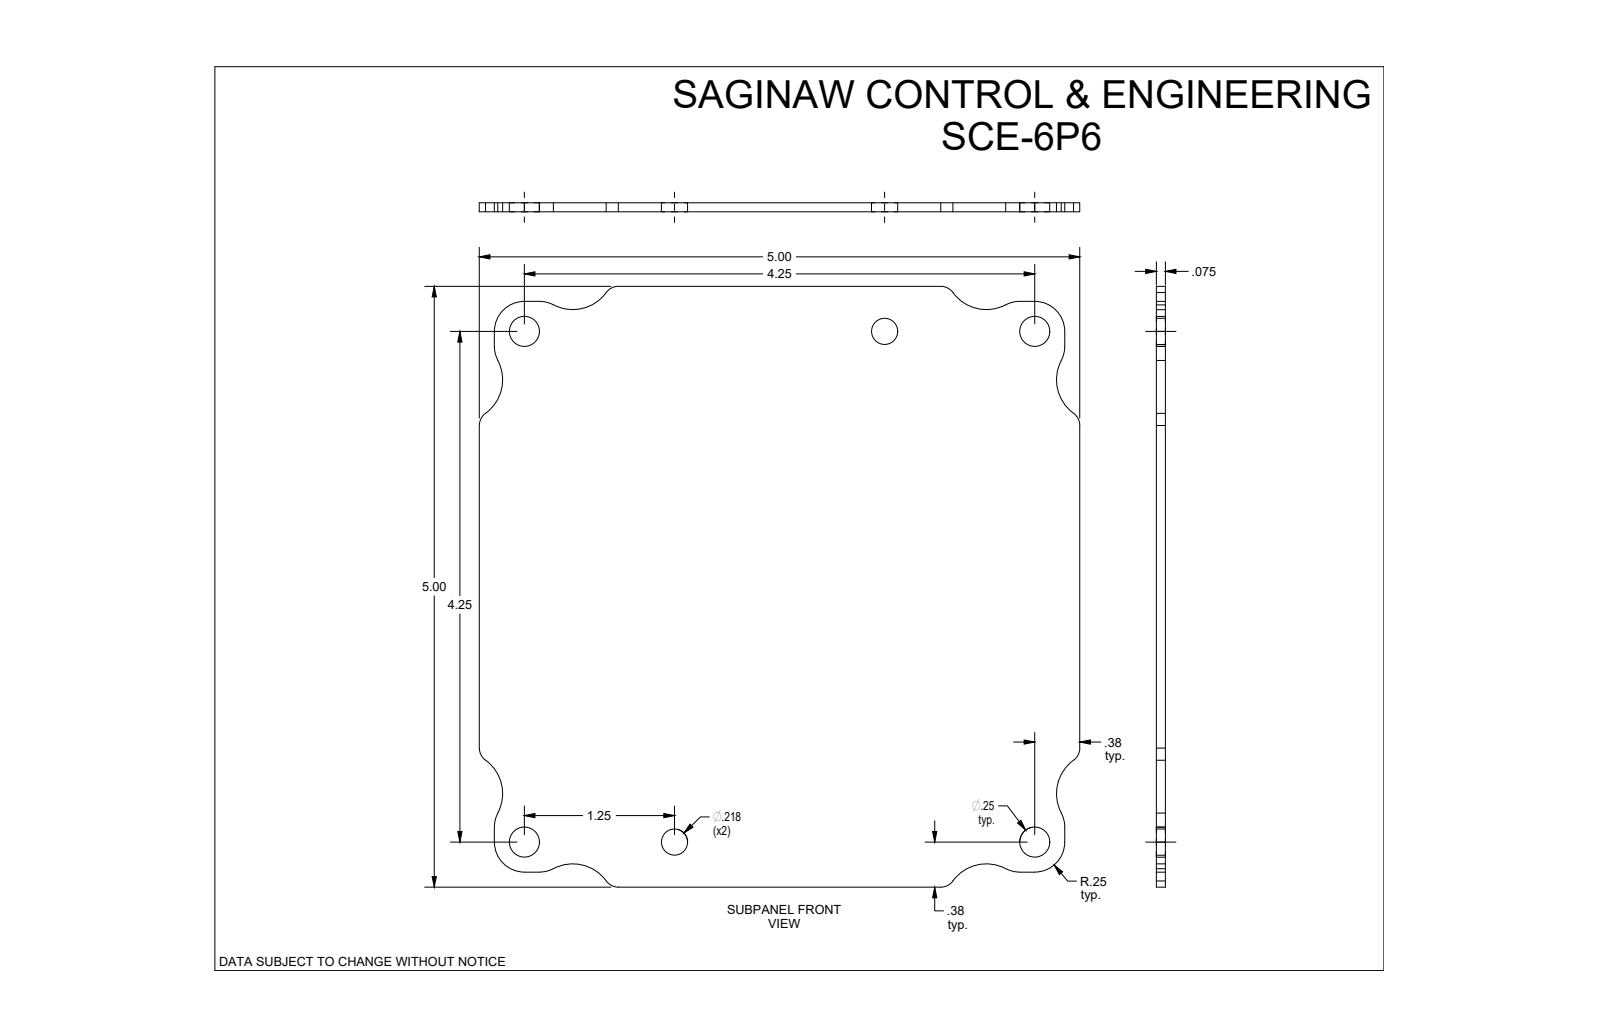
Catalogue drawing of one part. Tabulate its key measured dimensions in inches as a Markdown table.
| quantity | value |
| --- | --- |
| part name | SCE-6P6 |
| STEP written by | SolidWorks 2019 (CONFIG_CONTROL_DESIGN) |
| units | inches |
| bodies | 1 solid, 48 faces (14 planar, 34 cylindrical, 0 other) |
| overall size | 5 × 5 × 0.075 |
| volume | 1.765 in³ |
| surface area | 48.83 in² |
| round holes (diameter × count) | 0.25 × 4, 0.218 × 2 |
| partial cylindrical surfaces (radius × count) | 0.25 × 12, 0.125 × 8, 0.344 × 8 |
| main face-to-face distances | 0.075, 5, 0.125, 4.875, 4.75 |
| hole center spacings | 4.25, 1.25, 3, 4.43, 5.202, 6.01, 4.596 |
